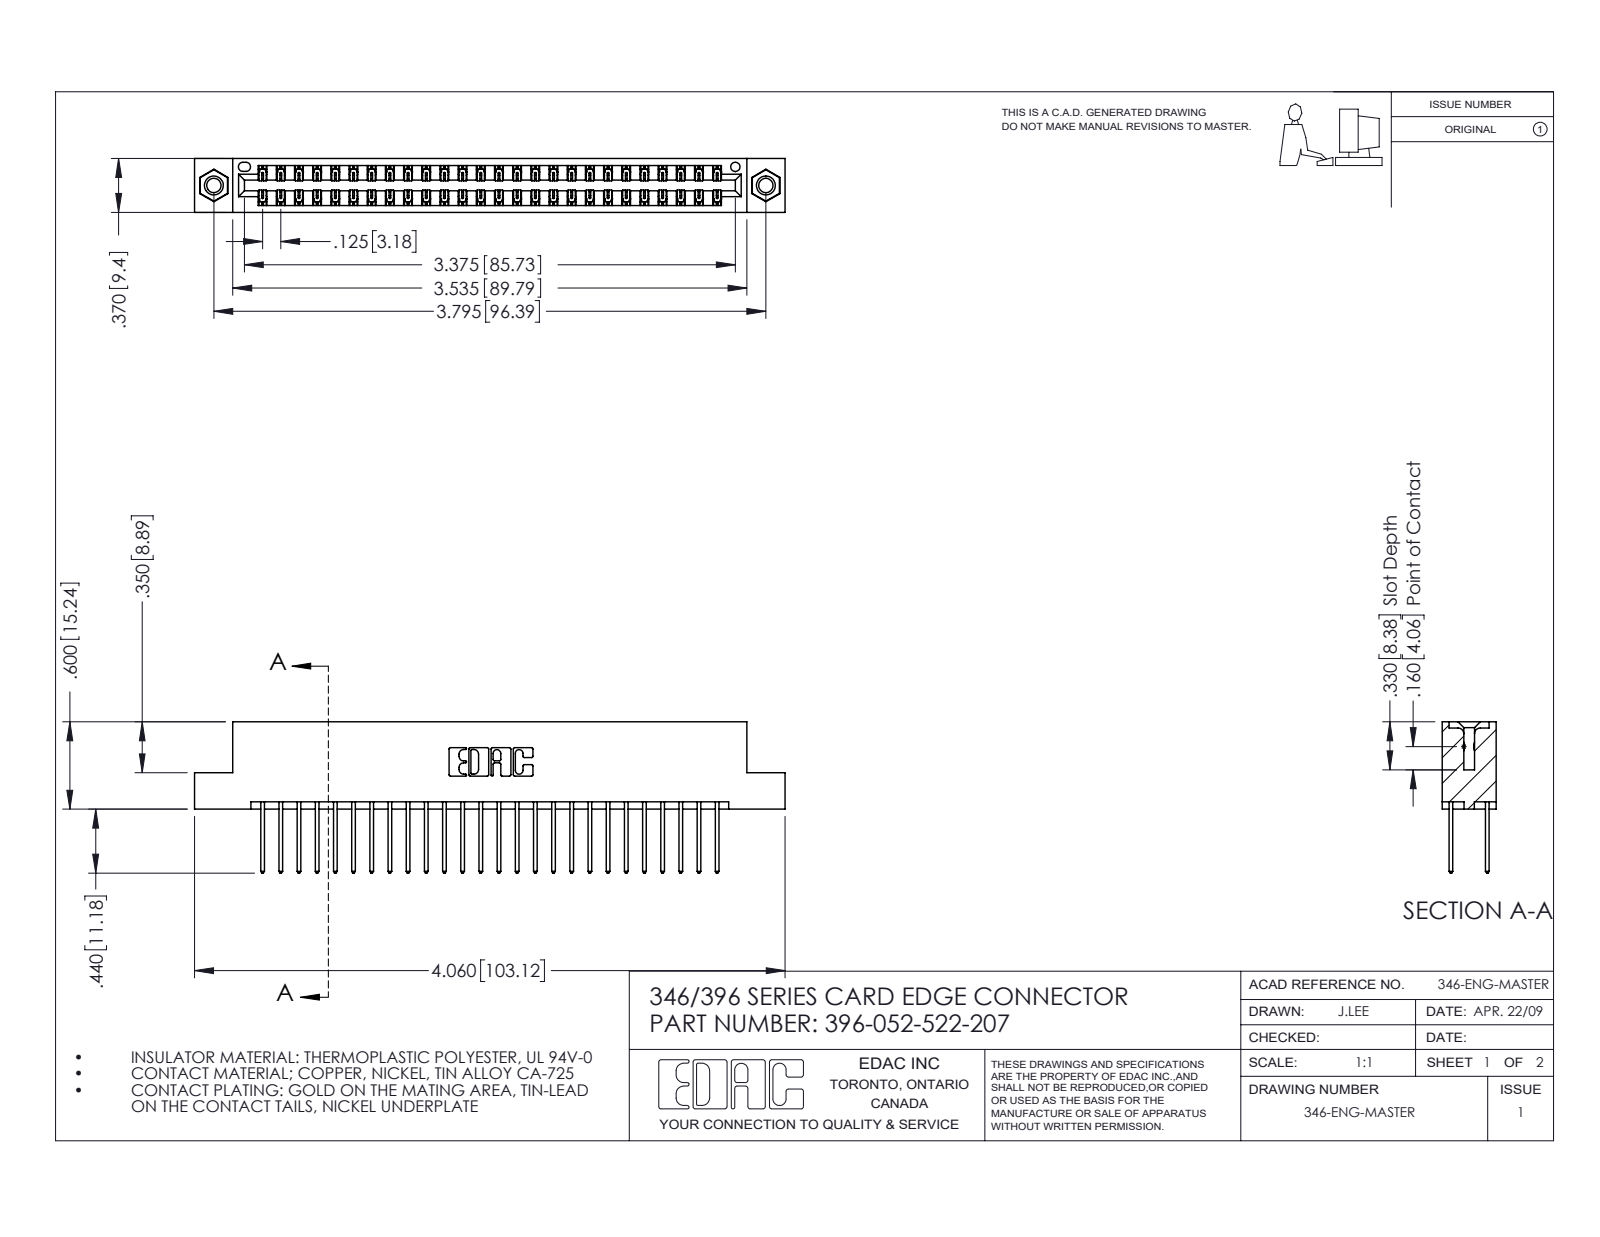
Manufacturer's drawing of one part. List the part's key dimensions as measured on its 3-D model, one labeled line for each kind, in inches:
Part name (STEP PRODUCT): 396-052-522-207; 345-292-001_345-293-122; 346 Part_Flush Mounting Lugs - 0.156 Dia-TI; 345-250-001_345-250-005-103
STEP written by: SolidWorks 2016 (CONFIG_CONTROL_DESIGN)
Units: inches
Bodies: 55 solids, 2886 faces (1928 planar, 942 cylindrical, 16 other)
Overall size (bounding box): 4.06 × 1.04 × 0.37
Volume: 0.613 in³ · Surface area: 22.04 in²
Round holes (diameter × count): ⌀0.098 ×2, ⌀0.125 ×2, ⌀0.156 ×2, ⌀0.064 ×1
Round bosses / shafts (diameter × count): ⌀0.155 ×2
Partial cylindrical surfaces — rounded edges, fillets, slot ends (radius × count): R0.006 ×78, R0.01 ×52, R0.01 ×22, R0.007 ×6, R0.031 ×6, R0.026 ×3, R0.014 ×2, R0.022 ×2
Main face-to-face distances: 0.048, 0.322, 0.25, 0.37, 0.072, 0.298, 0.025, 0.275, 0.148, 0.222
Hole centre spacings: 0.246, 3.587, 3.795
